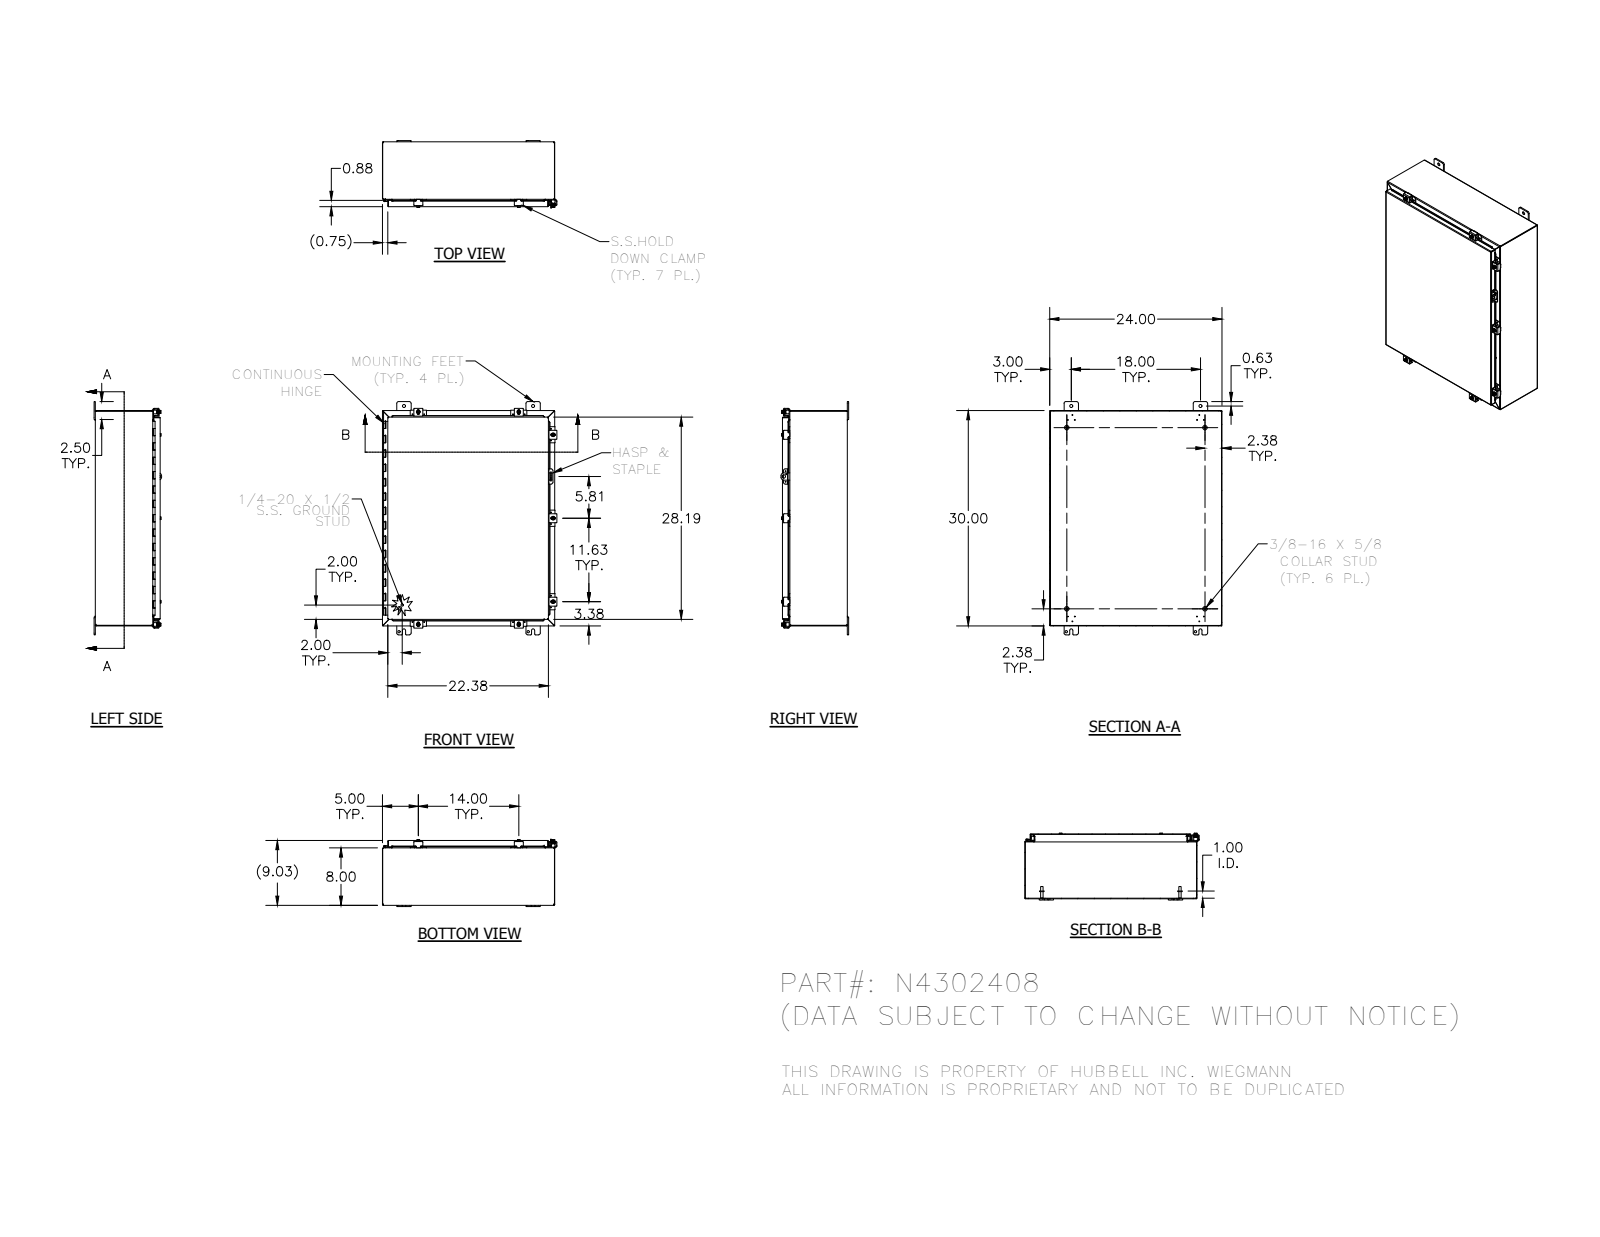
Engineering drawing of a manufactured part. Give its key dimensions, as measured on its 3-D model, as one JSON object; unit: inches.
{"part_name": "30824-1_1; 388116_1; 38420_1; 328106P-1_1 (+8 more)", "step_written_by": "SolidWorks 2014 (AUTOMOTIVE_DESIGN)", "units": "inches", "bodies": {"solids": 52, "faces": 2311, "planar": 889, "cylindrical": 1039, "other": 383}, "overall_size": [32.5, 24.311, 9.41], "volume_in3": 209, "surface_area_in2": 5474, "round_holes": [[0.11, 17], [0.12, 12], [0.211, 7], [0.281, 7], [0.3, 7], [0.313, 4], [0.438, 4], [0.125, 1], [0.156, 1], [0.5, 1]], "round_bosses_or_shafts": [[0.25, 9], [0.52, 7], [0.5, 7], [0.35, 7], [0.625, 4], [0.33, 4], [0.115, 2], [0.337, 1]], "partial_cylinders_radius": [[0.03, 83], [0.062, 41], [0.125, 37], [0.25, 33], [0.031, 23], [0.105, 23], [0.063, 14], [0.141, 14]], "face_to_face_distances": [0.074, 8.959, 8.885, 9.033, 23.926, 29.926, 7.926, 1.033, 24, 23.852], "hole_center_spacings": [18, 0.876, 0.759, 0.94, 0.969, 1.995, 17.37, 18.339]}
